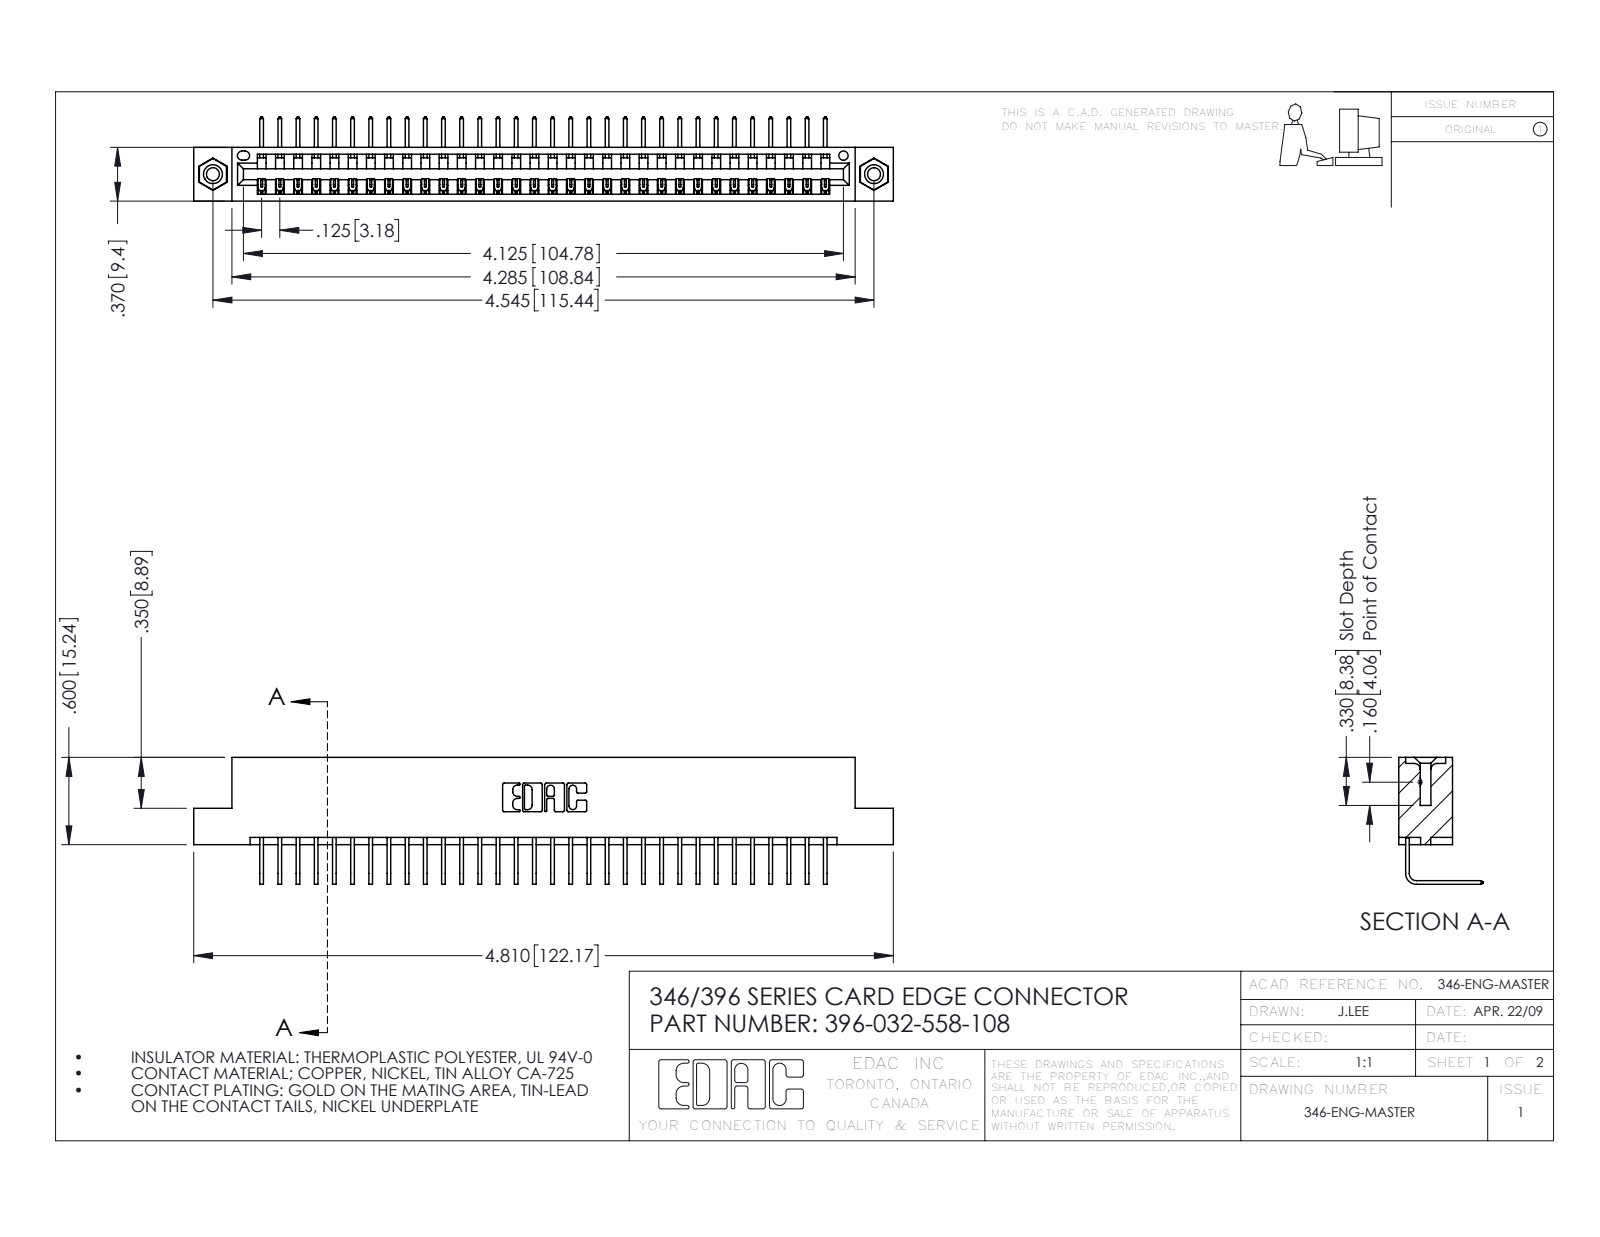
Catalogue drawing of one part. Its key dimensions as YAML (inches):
part_name: "345-292-001_558 Tail - 2; 345-250-001_345-250-003-102; 346 Part_Flush Mounting Lugs - 0.156 Dia-TI; 396-032-558-108"
step_written_by: "SolidWorks 2016 (CONFIG_CONTROL_DESIGN)"
units: inches
bodies: {solids: 35, faces: 2102, planar: 1452, cylindrical: 634, other: 16}
overall_size: [4.81, 0.873, 0.58]
volume: 0.716
surface_area: 23.57
round_holes:
  - {diameter: 0.089, count: 2}
  - {diameter: 0.125, count: 2}
  - {diameter: 0.156, count: 2}
  - {diameter: 0.064, count: 1}
round_bosses_or_shafts:
  - {diameter: 0.155, count: 2}
partial_cylinders:
  - {radius: 0.006, count: 64}
  - {radius: 0.01, count: 22}
  - {radius: 0.007, count: 6}
  - {radius: 0.031, count: 6}
  - {radius: 0.026, count: 3}
  - {radius: 0.031, count: 2}
  - {radius: 0.04, count: 2}
  - {radius: 0.014, count: 1}
face_to_face_distances: [0.322, 0.048, 0.37, 0.25, 0.298, 0.025, 0.072, 0.148, 0.222, 0.1]
hole_center_spacings: [0.246, 4.337, 4.545]
